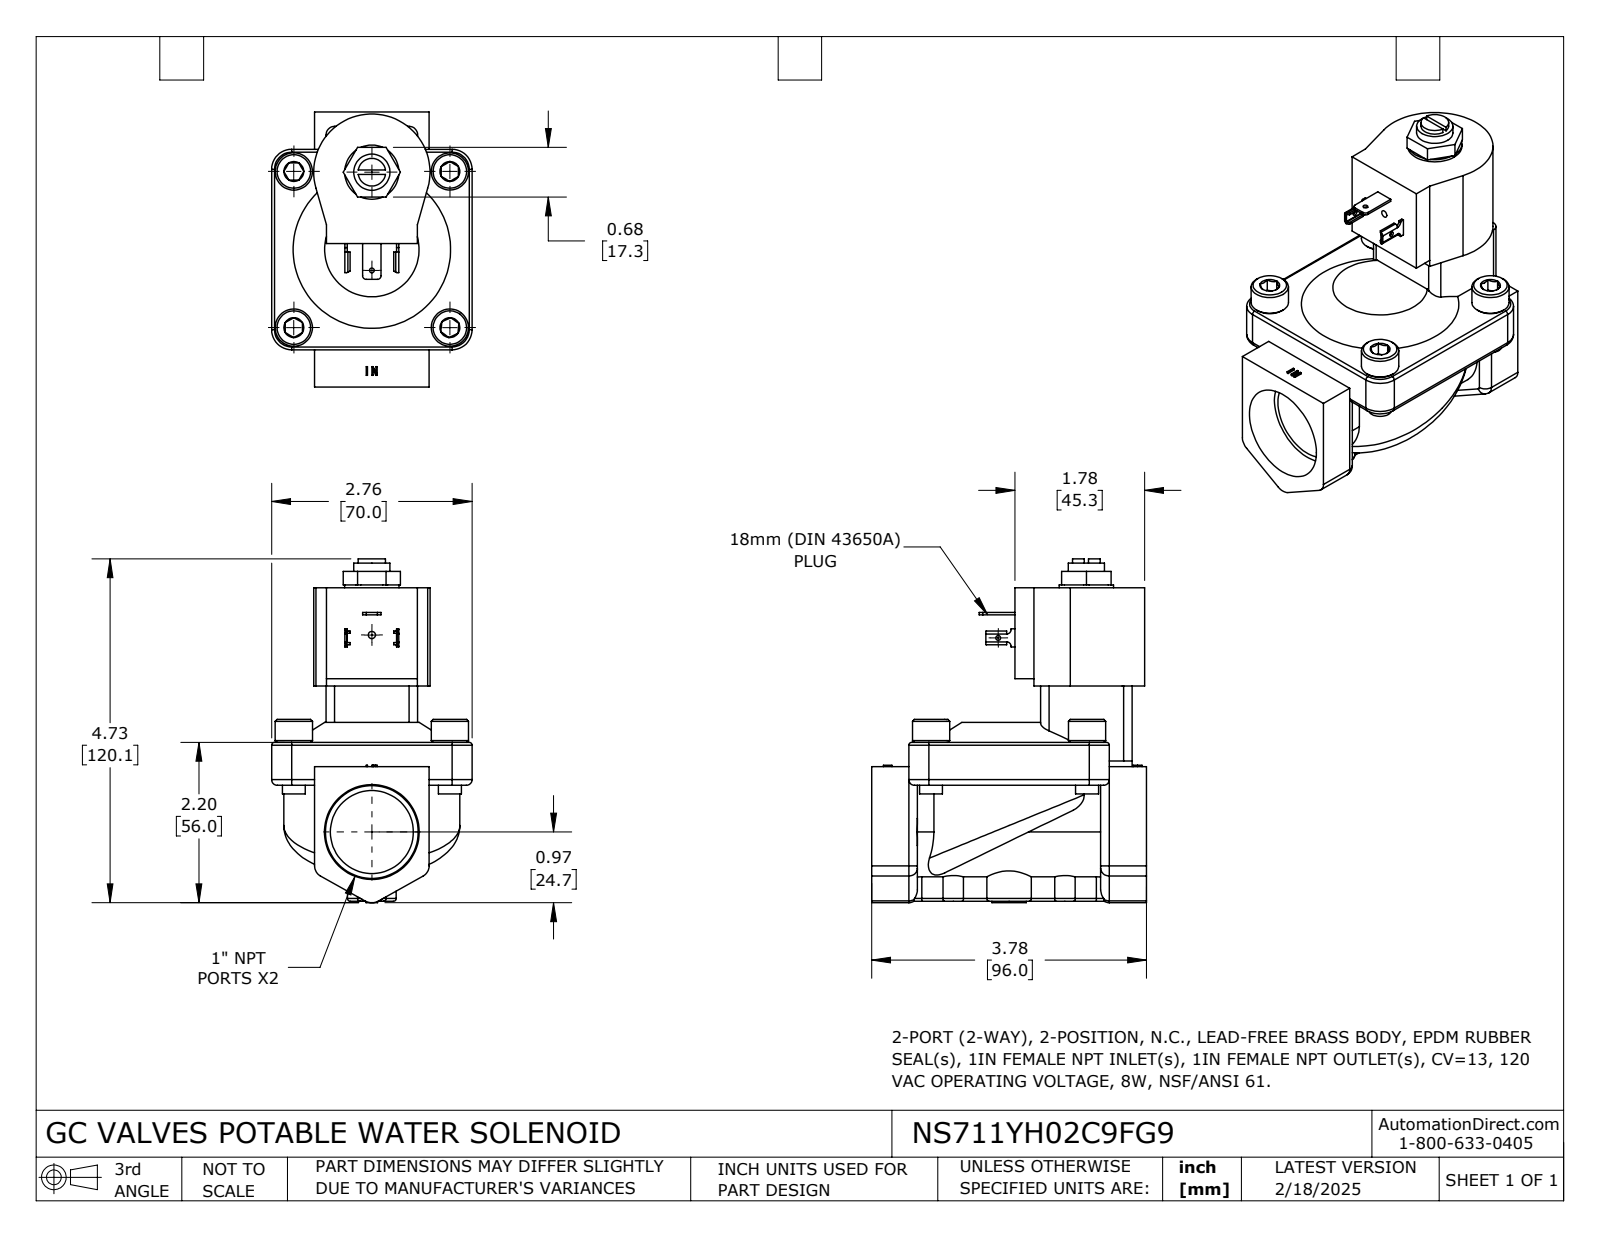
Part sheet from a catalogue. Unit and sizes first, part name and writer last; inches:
Units: inches
Overall size (bounding box): 4.727 × 3.78 × 2.756
Round holes (diameter × count): ⌀0.066 ×1, ⌀0.067 ×1, ⌀0.1 ×1, ⌀1.141 ×1
Round bosses / shafts (diameter × count): ⌀0.512 ×4, ⌀0.315 ×4, ⌀0.746 ×1, ⌀0.499 ×1, ⌀0.38 ×1
Partial cylindrical surfaces — rounded edges, fillets, slot ends (radius × count): R0.118 ×12, R0.039 ×6, R0.006 ×4, R0.041 ×4, R0.079 ×4, R0.276 ×4, R0.197 ×3, R0.05 ×2
Main face-to-face distances: 0.591, 0.157, 1.417, 0.748, 2.008, 2.165, 2.126, 0.276, 1.26, 0.256
Hole centre spacings: 2.707
Volume: 15.95 in³ · Surface area: 66.39 in²
Bodies: 1 solid, 412 faces (199 planar, 115 cylindrical, 98 other)
Part name (STEP PRODUCT): NS711YH02C9FG9
STEP written by: SolidWorks 2024 (CONFIG_CONTROL_DESIGN)
